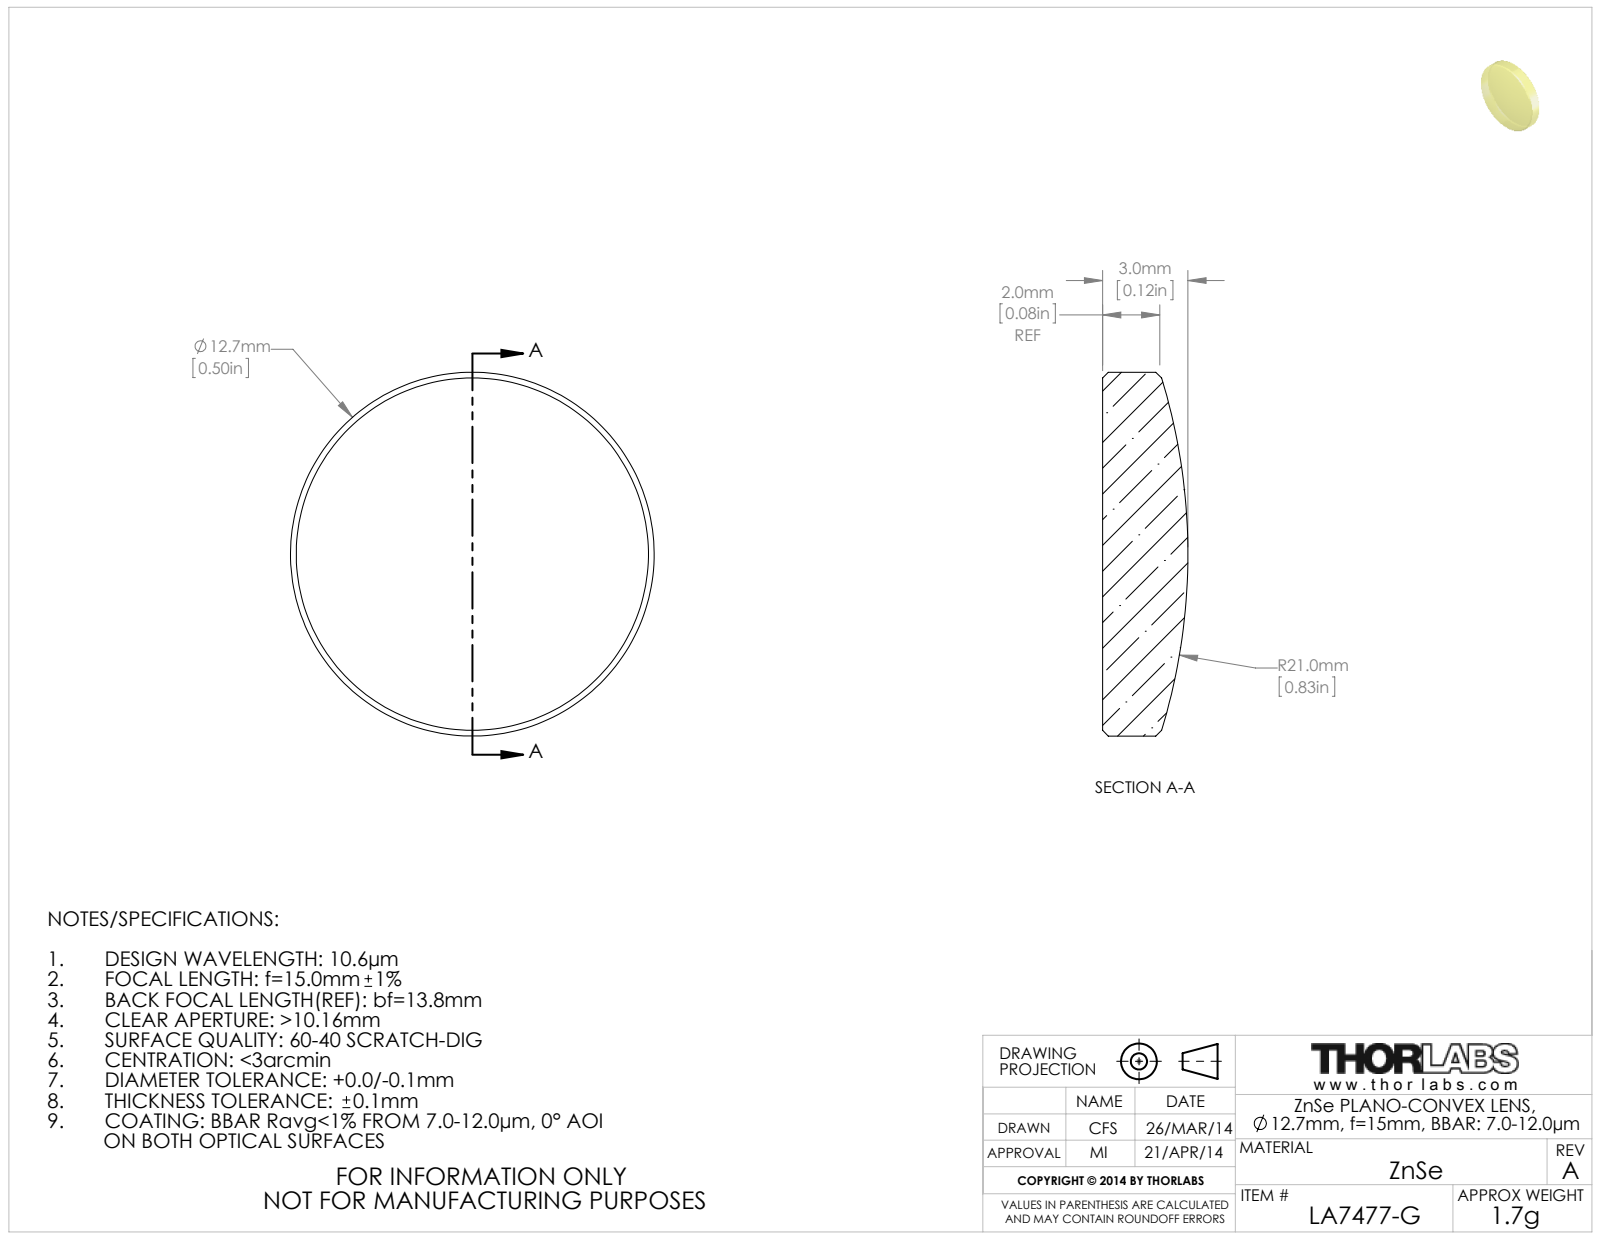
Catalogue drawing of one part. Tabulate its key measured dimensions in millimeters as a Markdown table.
| quantity | value |
| --- | --- |
| part name | TTN023909-E0W |
| STEP written by | SolidWorks 2012 (CONFIG_CONTROL_DESIGN) |
| units | millimeters |
| bodies | 1 solid, 9 faces (1 planar, 2 cylindrical, 6 other) |
| overall size | 12.7 × 12.7 × 3 |
| volume | 310 mm³ |
| surface area | 329 mm² |
| round bosses / shafts (diameter × count) | 12.7 × 1 |
